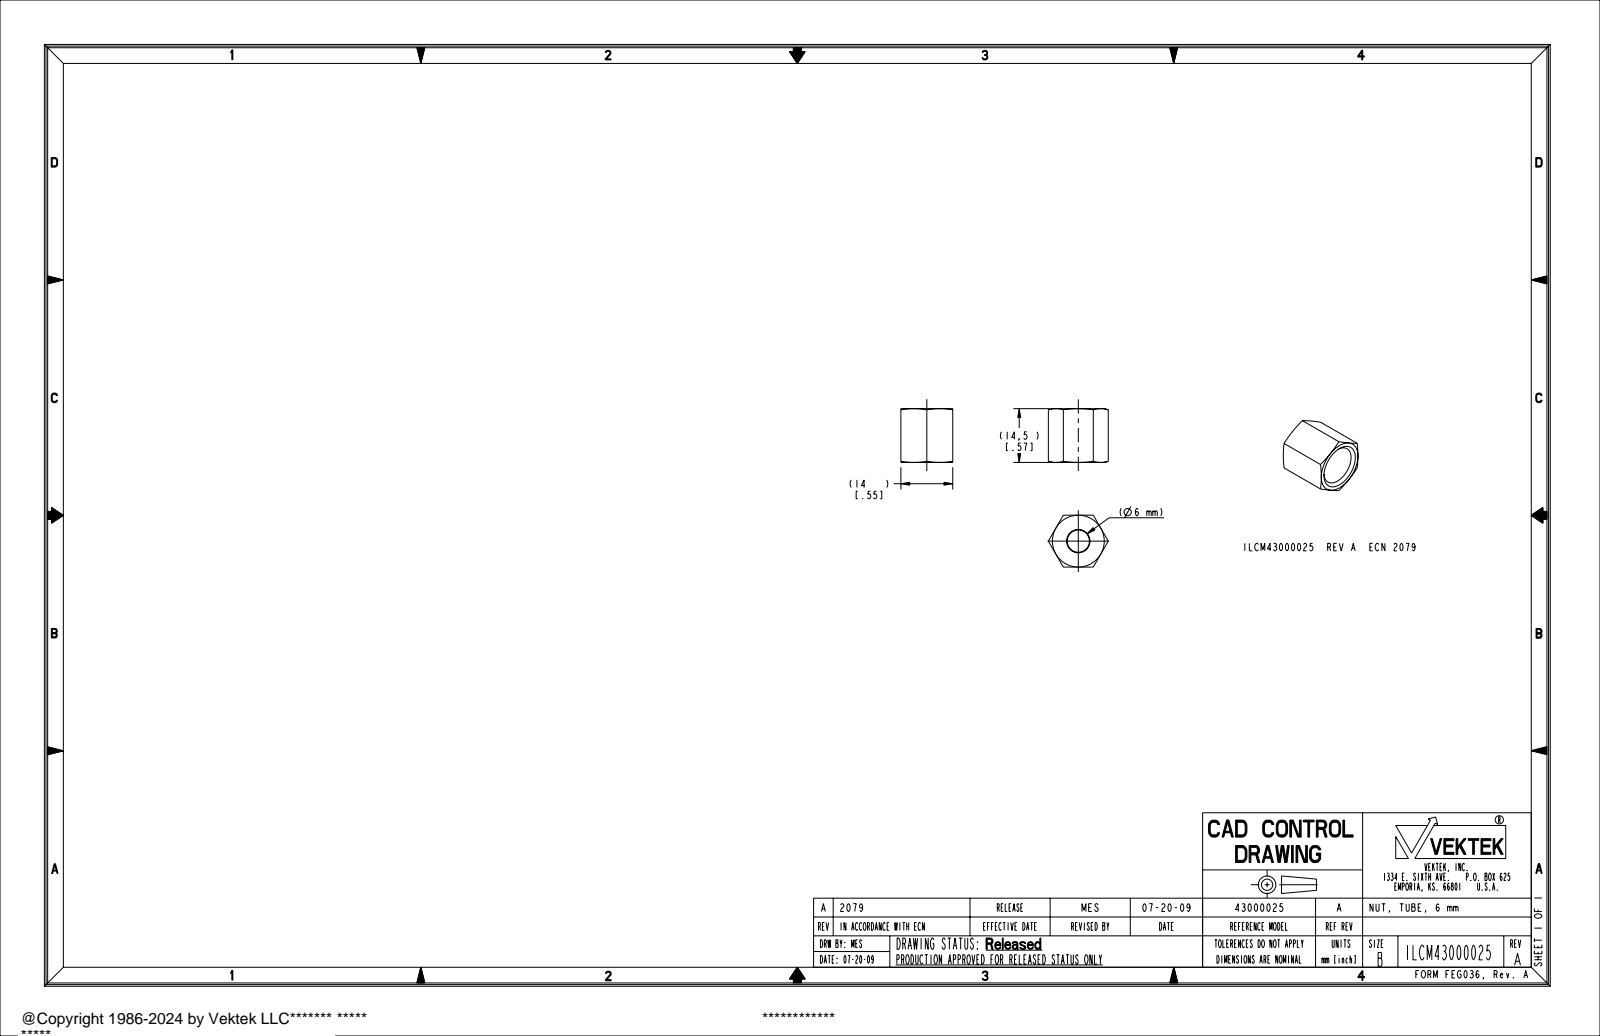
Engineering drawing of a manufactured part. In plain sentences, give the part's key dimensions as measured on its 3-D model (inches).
The part is named "ILCM43000025". Its 3-D file was written by "PRO/ENGINEER BY PARAMETRIC TECHNOLOGY CORPORATION, 2007460 (AUTOMOTIVE_DESIGN_CC2)". It is 1 solid with 79 faces: 38 planar, 23 cylindrical and 18 other. Overall it measures 0.636 by 0.571 by 0.551 inches. Its volume is 0.086 cubic inches and its surface area 2.699 square inches. Round holes: 1 of diameter 0.198, 1 of diameter 0.236, 1 of diameter 0.409. Round bosses or shafts: 1 of diameter 0.455. Partial cylindrical surfaces (rounded edges, fillets, slot ends): 4 of radius 0.022, 2 of radius 0.014, 2 of radius 0.277, 2 of radius 0.299, 2 of radius 0.315, 1 of radius 0.043. The main face-to-face distances are 0.551, 0.571, 0.539, 0.541, 0.53, 0.341, 0.23, 0.528, 0.531, 0.028.
